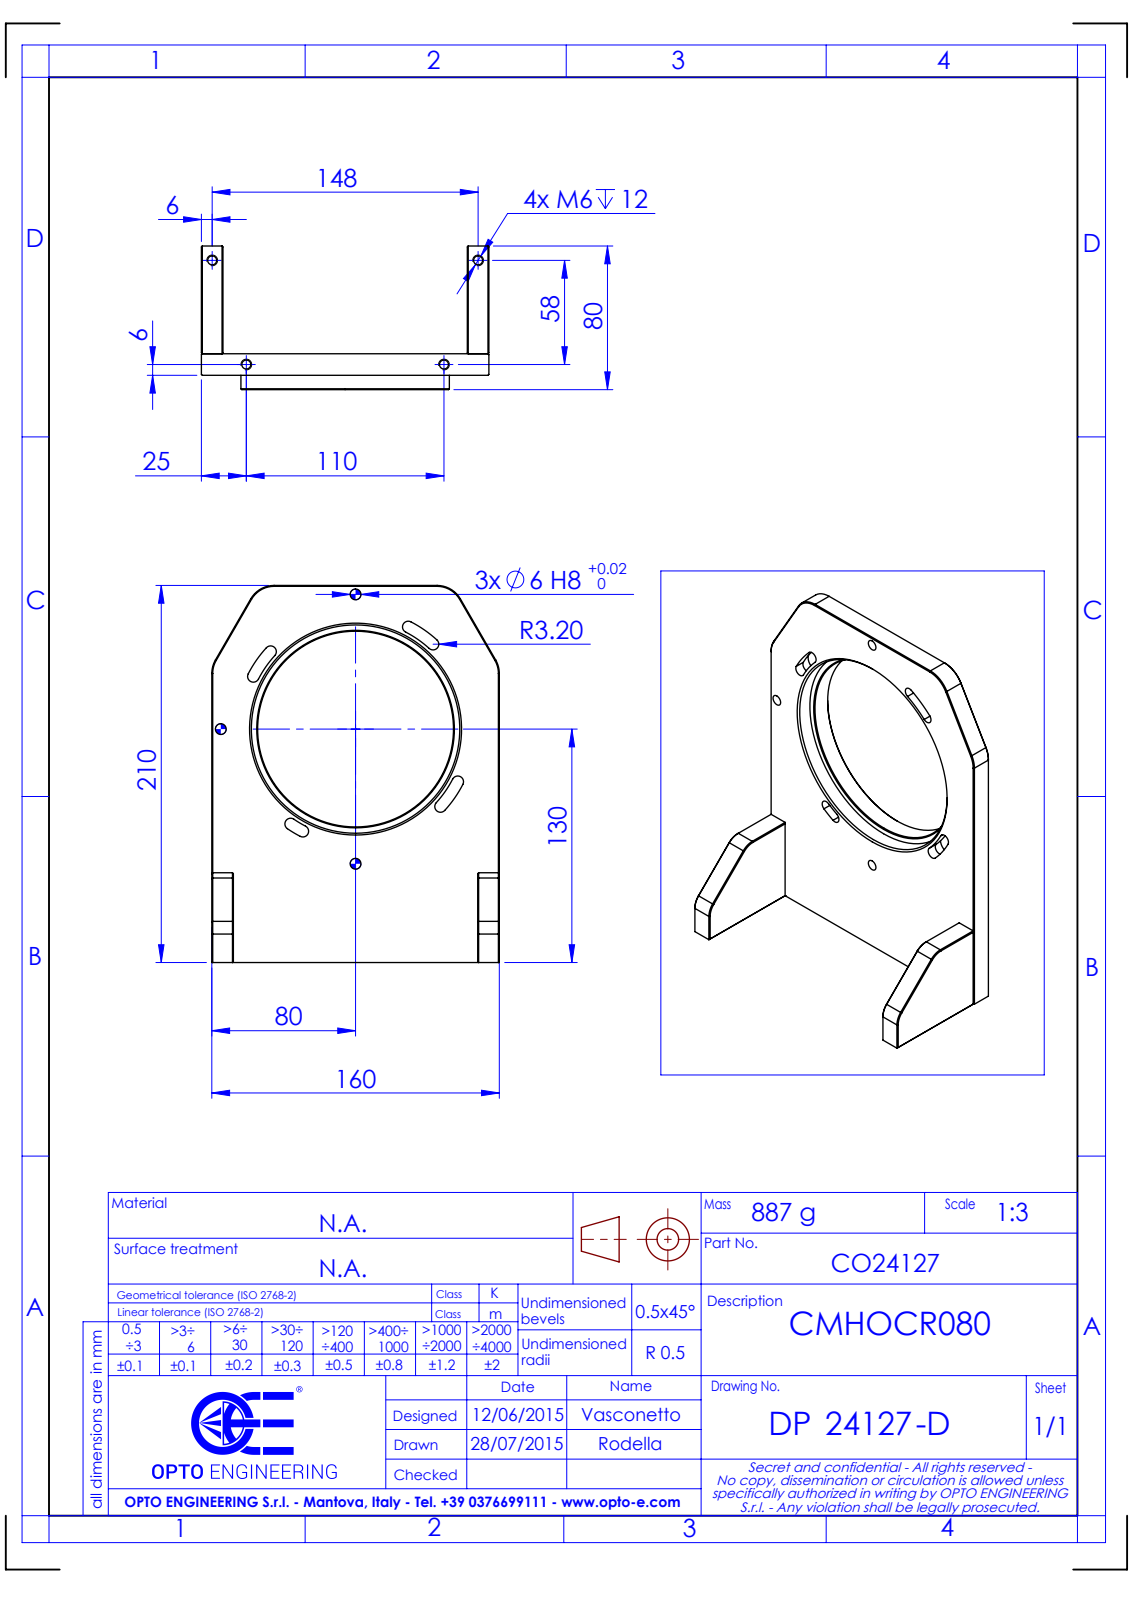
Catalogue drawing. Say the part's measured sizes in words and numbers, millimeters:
The part is named "DP24127-D_CMHOCR080". Its 3-D file was written by "SolidWorks 2021 (CONFIG_CONTROL_DESIGN)". It is 0 solids with 206 faces: 82 planar, 84 cylindrical and 40 other. Overall it measures 210 by 160 by 80 millimeters. Round holes: 4 of diameter 5, 4 of diameter 11, 3 of diameter 6, 1 of diameter 109, 1 of diameter 116. Round bosses or shafts: 4 of diameter 10. Partial cylindrical surfaces (rounded edges, fillets, slot ends): 8 of radius 3.2, 8 of radius 5.5, 4 of radius 15, 2 of radius 10, 1 of radius 58.5, 1 of radius 60.8, 1 of radius 67.2, 1 of radius 69.5. The main face-to-face distances are 12, 148, 160, 136, 3, 9, 210, 8, 11, 20. The hole center spacings are 75, 148, 30, 61.03, 75.5, 86.61, 106.07, 116.52.
